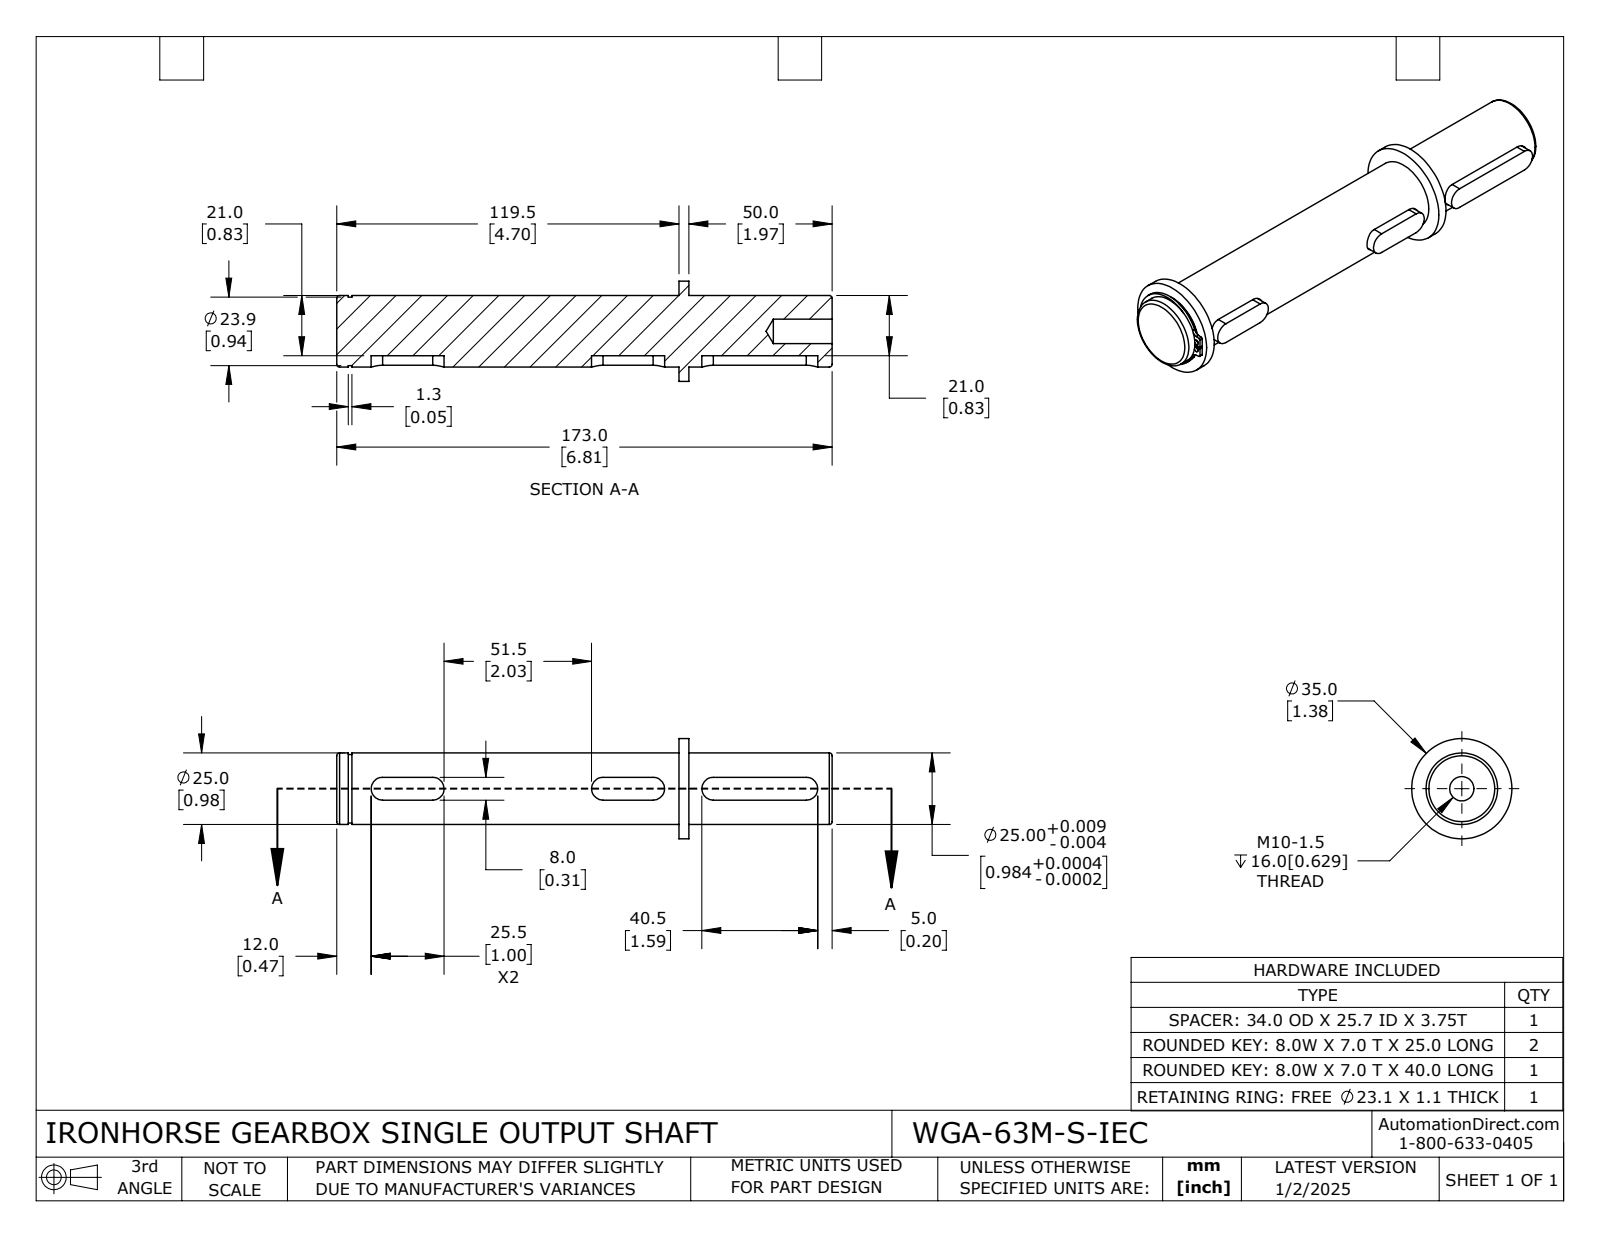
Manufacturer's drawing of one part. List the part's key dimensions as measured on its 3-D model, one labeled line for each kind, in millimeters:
Part name (STEP PRODUCT): WGA-63M-S-IEC
STEP written by: SolidWorks 2024 (CONFIG_CONTROL_DESIGN)
Units: millimetres
Bodies: 1 solid, 42 faces (15 planar, 21 cylindrical, 6 other)
Overall size (bounding box): 173 × 35 × 35
Volume: 82 649 mm³ · Surface area: 16 907 mm²
Round holes (diameter × count): ⌀8.5 ×1
Round bosses / shafts (diameter × count): ⌀35 ×1, ⌀25 ×1, ⌀23.9 ×1
Partial cylindrical surfaces — rounded edges, fillets, slot ends (radius × count): R4 ×6
Main face-to-face distances: 3.5, 119.5, 123, 173, 53.5, 50, 8, 5.3, 114.2, 117.7
